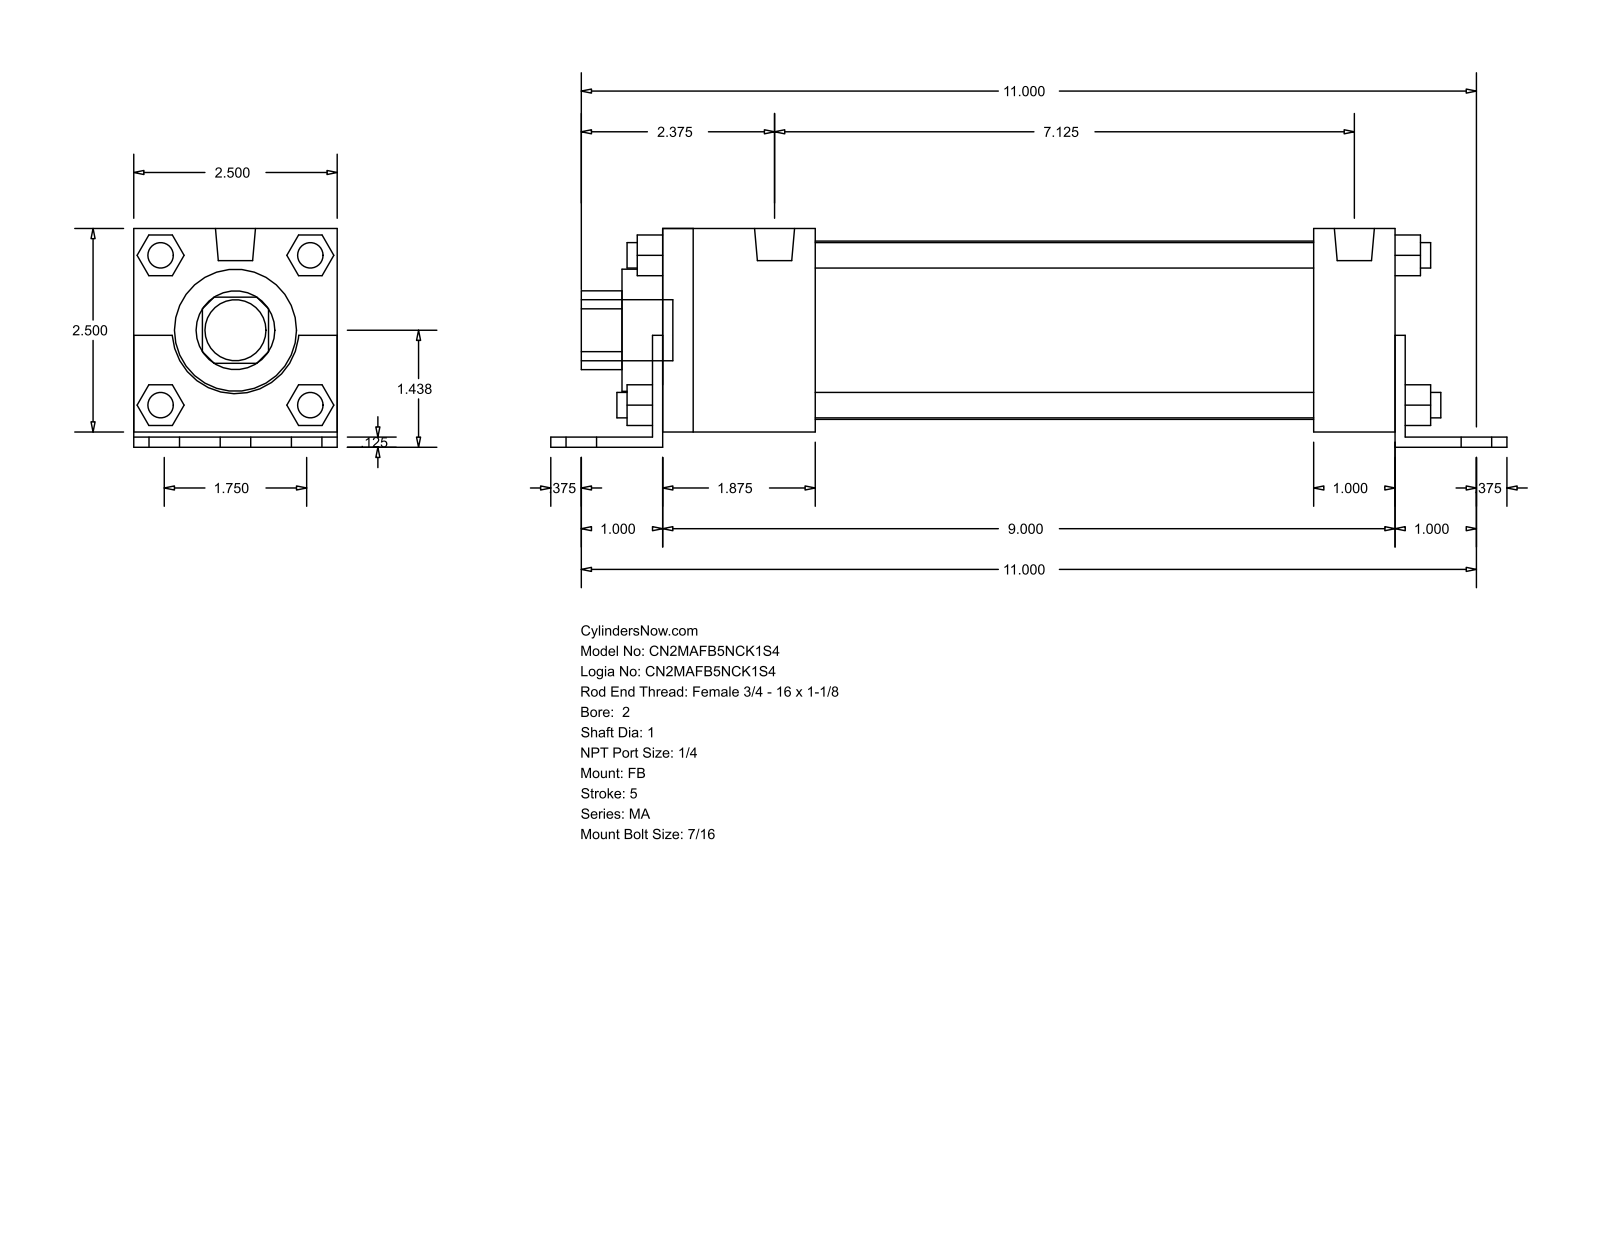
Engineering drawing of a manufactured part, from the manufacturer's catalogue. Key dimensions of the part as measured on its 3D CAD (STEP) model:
Part name (STEP PRODUCT): MA_FB__0200_1
STEP written by: GSSL Pune (CONFIG_CONTROL_DESIGN)
Units: millimetres
Bodies: 0 solids, 140 faces (105 planar, 35 cylindrical, 0 other)
Overall size (bounding box): 298.45 × 68.26 × 63.5
Round holes (diameter × count): ⌀25.4 ×1, ⌀38.1 ×1, ⌀55.63 ×1
Round bosses / shafts (diameter × count): ⌀7.94 ×8, ⌀11.11 ×6, ⌀12.49 ×2, ⌀19.05 ×1
Partial cylindrical surfaces — rounded edges, fillets, slot ends (radius × count): R12.29 ×1, R19.81 ×1
Main face-to-face distances: 63.5, 3.17, 4.76, 68.26, 1.59, 65.09, 12.7, 3.18, 228.6, 231.78
